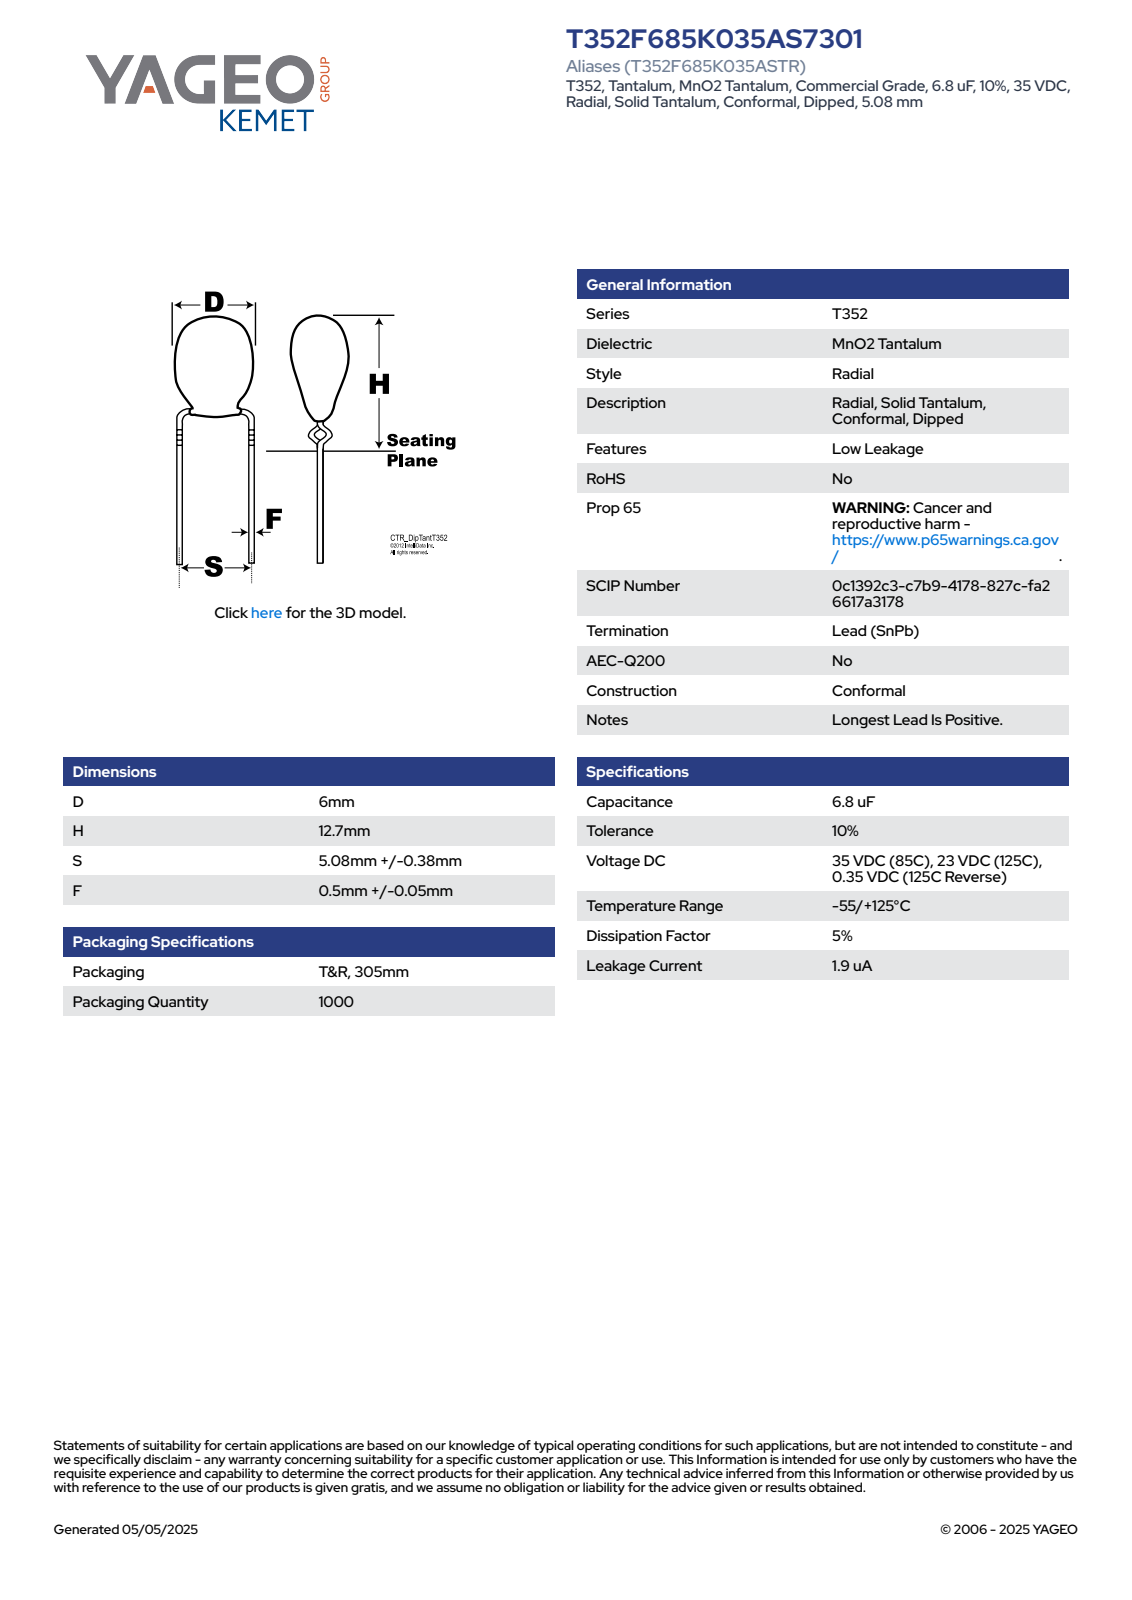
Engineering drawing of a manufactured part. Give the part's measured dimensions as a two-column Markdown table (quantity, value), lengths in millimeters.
| quantity | value |
| --- | --- |
| part name | CTR_T352_D6H12.7S5.08LL5.56F0.55 |
| STEP written by | SolidWorks 2014 (AUTOMOTIVE_DESIGN) |
| units | millimeters |
| bodies | 1 solid, 95 faces (26 planar, 16 cylindrical, 53 other) |
| overall size | 18.26 × 6 × 6 |
| volume | 243 mm³ |
| surface area | 236 mm² |
| round bosses / shafts (diameter × count) | 0.55 × 2, 6 × 1 |
| partial cylindrical surfaces (radius × count) | 0.28 × 1, 2.99 × 1 |
| main face-to-face distances | 9.96, 4.94, 5.02, 4.15, 0.79, 5.81, 0.64, 0.49, 4.3, 5.66 |
